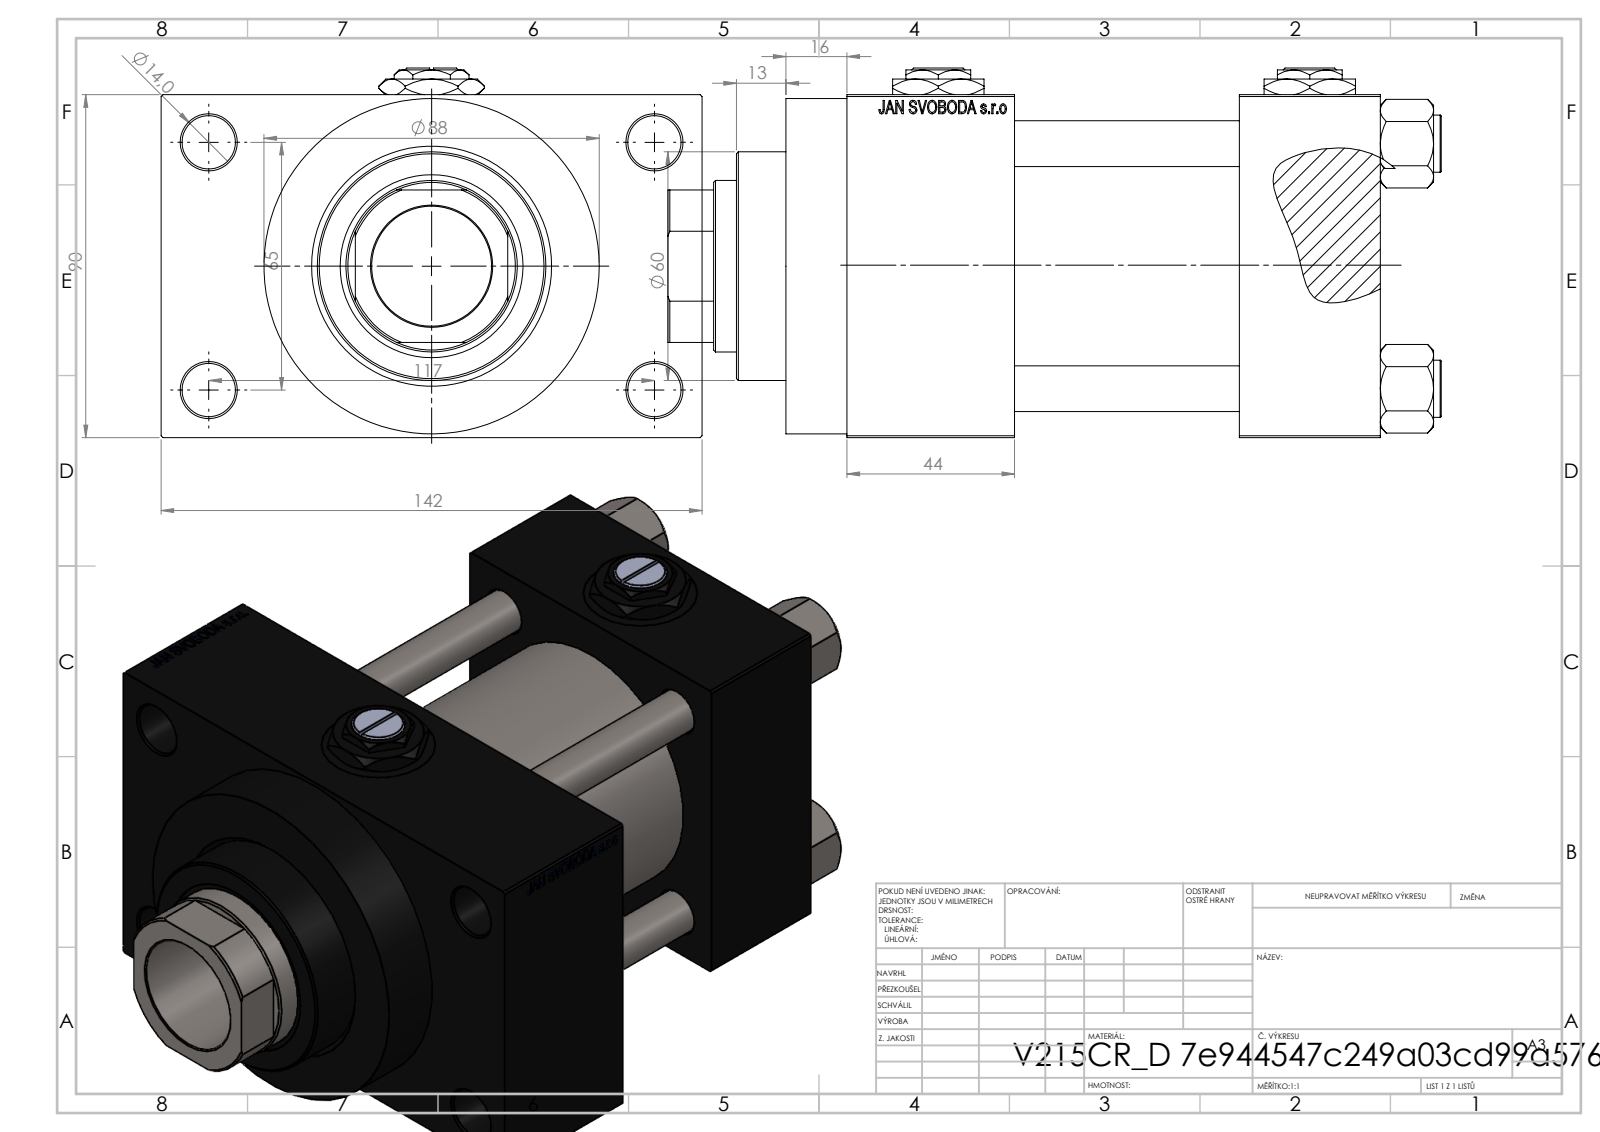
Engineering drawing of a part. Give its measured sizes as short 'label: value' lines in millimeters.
name: Zatka_pro_OIL_PORT; V215CR_D_Body; NUT_M5_D; V215_VC_A (+2 more)
written by: SolidWorks 2019 (CONFIG_CONTROL_DESIGN)
unit: mm
bodies: 13 solids, 1203 faces (544 planar, 97 cylindrical, 562 other)
size: 203 × 142 × 97
volume: 1 154 000 mm³; area: 217 012 mm²
holes: 4× ⌀12, 4× ⌀14, 4× ⌀20.96, 4× ⌀30, 3× ⌀7, 1× ⌀31.5, 1× ⌀45, 1× ⌀48, 1× ⌀50, 1× ⌀60, 1× ⌀63
bosses: 4× ⌀15, 1× ⌀88, 1× ⌀69
rounds: 1× R22
face distances: 90, 59, 37, 96, 26, 140, 44, 103, 116, 60
hole spacings: 26.35, 45.47, 64.3, 66.92, 69.81, 90.65, 111.34, 65
